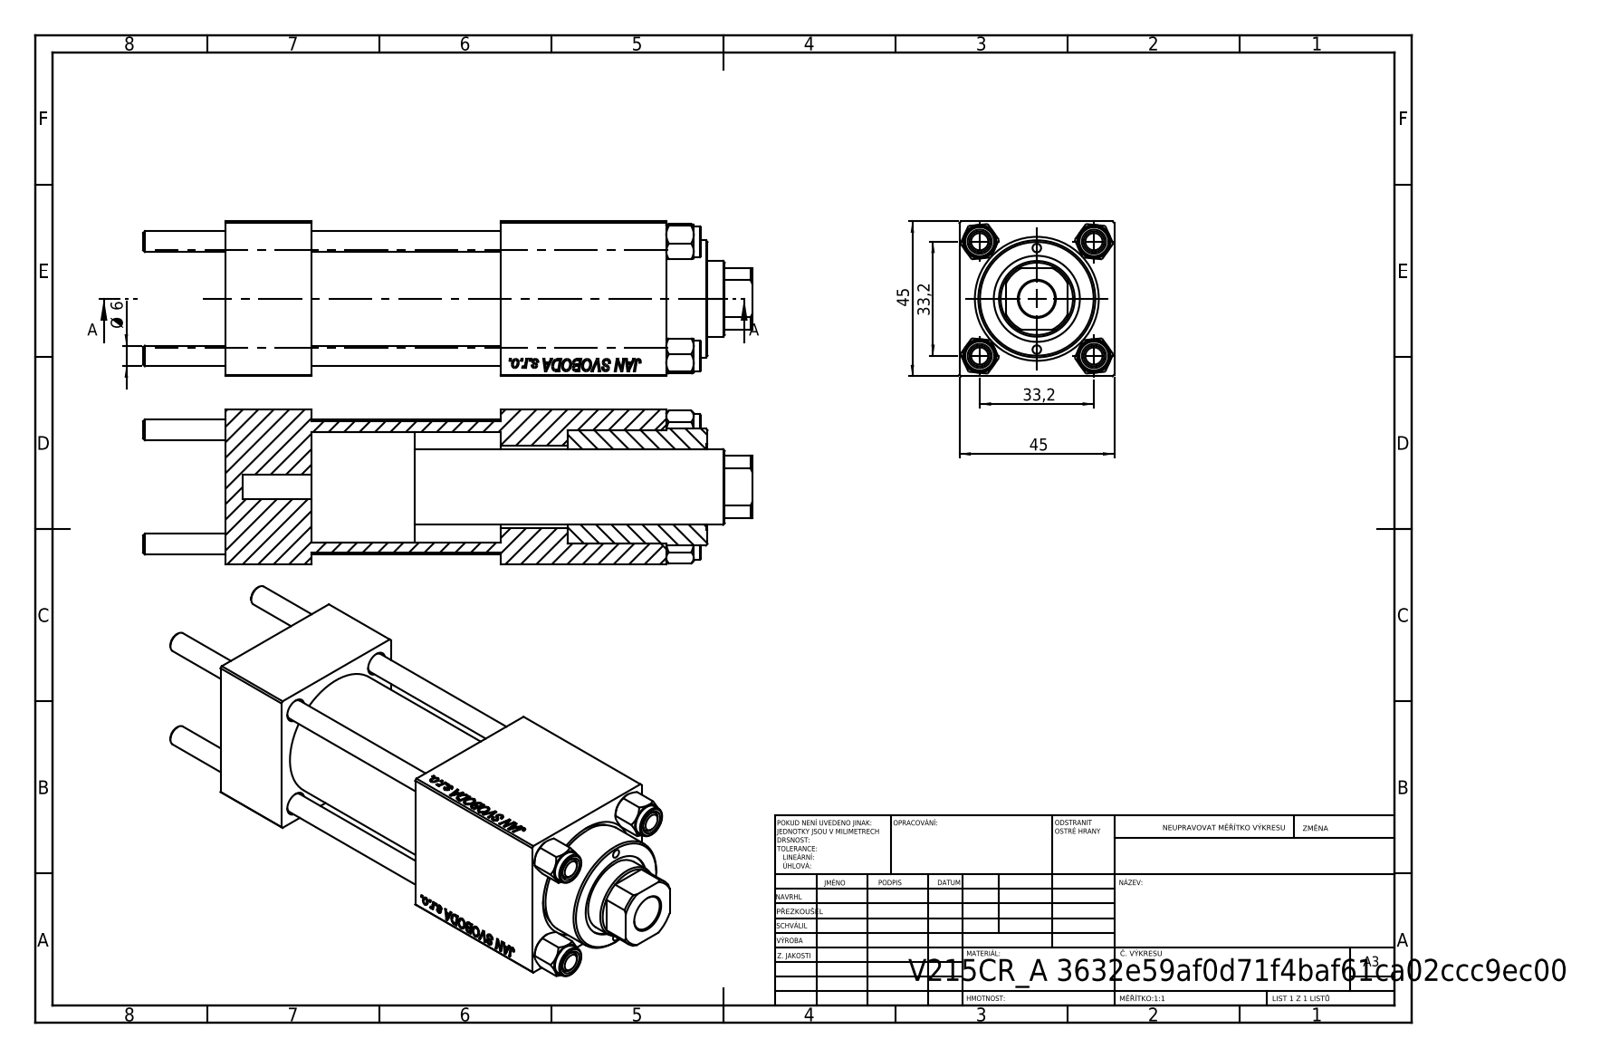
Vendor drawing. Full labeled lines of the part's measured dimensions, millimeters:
Part name (STEP PRODUCT): CR025_012_A_0_G_A_G_M_020_+#_##_TYCINKA; V215_VC_A; NUT_M5; V215CR_VCP (+1 more)
STEP written by: SolidWorks 2019 (CONFIG_CONTROL_DESIGN)
Units: millimetres
Bodies: 11 solids, 1139 faces (521 planar, 82 cylindrical, 536 other)
Overall size (bounding box): 177 × 45 × 45
Volume: 218 223 mm³ · Surface area: 79 131 mm²
Round holes (diameter × count): ⌀6 ×4, ⌀2.5 ×2, ⌀7 ×2, ⌀13.16 ×2, ⌀20 ×2, ⌀10.5 ×1, ⌀22 ×1, ⌀24 ×1, ⌀25 ×1, ⌀32 ×1, ⌀33 ×1
Round bosses / shafts (diameter × count): ⌀9 ×4, ⌀38 ×1, ⌀34 ×1
Partial cylindrical surfaces — rounded edges, fillets, slot ends (radius × count): R10.5 ×1
Main face-to-face distances: 45, 25, 55, 128, 80, 103, 48, 99.3, 74.3, 19.3
Hole centre spacings: 16.7, 23.48, 33.2, 35.47, 14.75, 46.95, 29.5, 80.5
